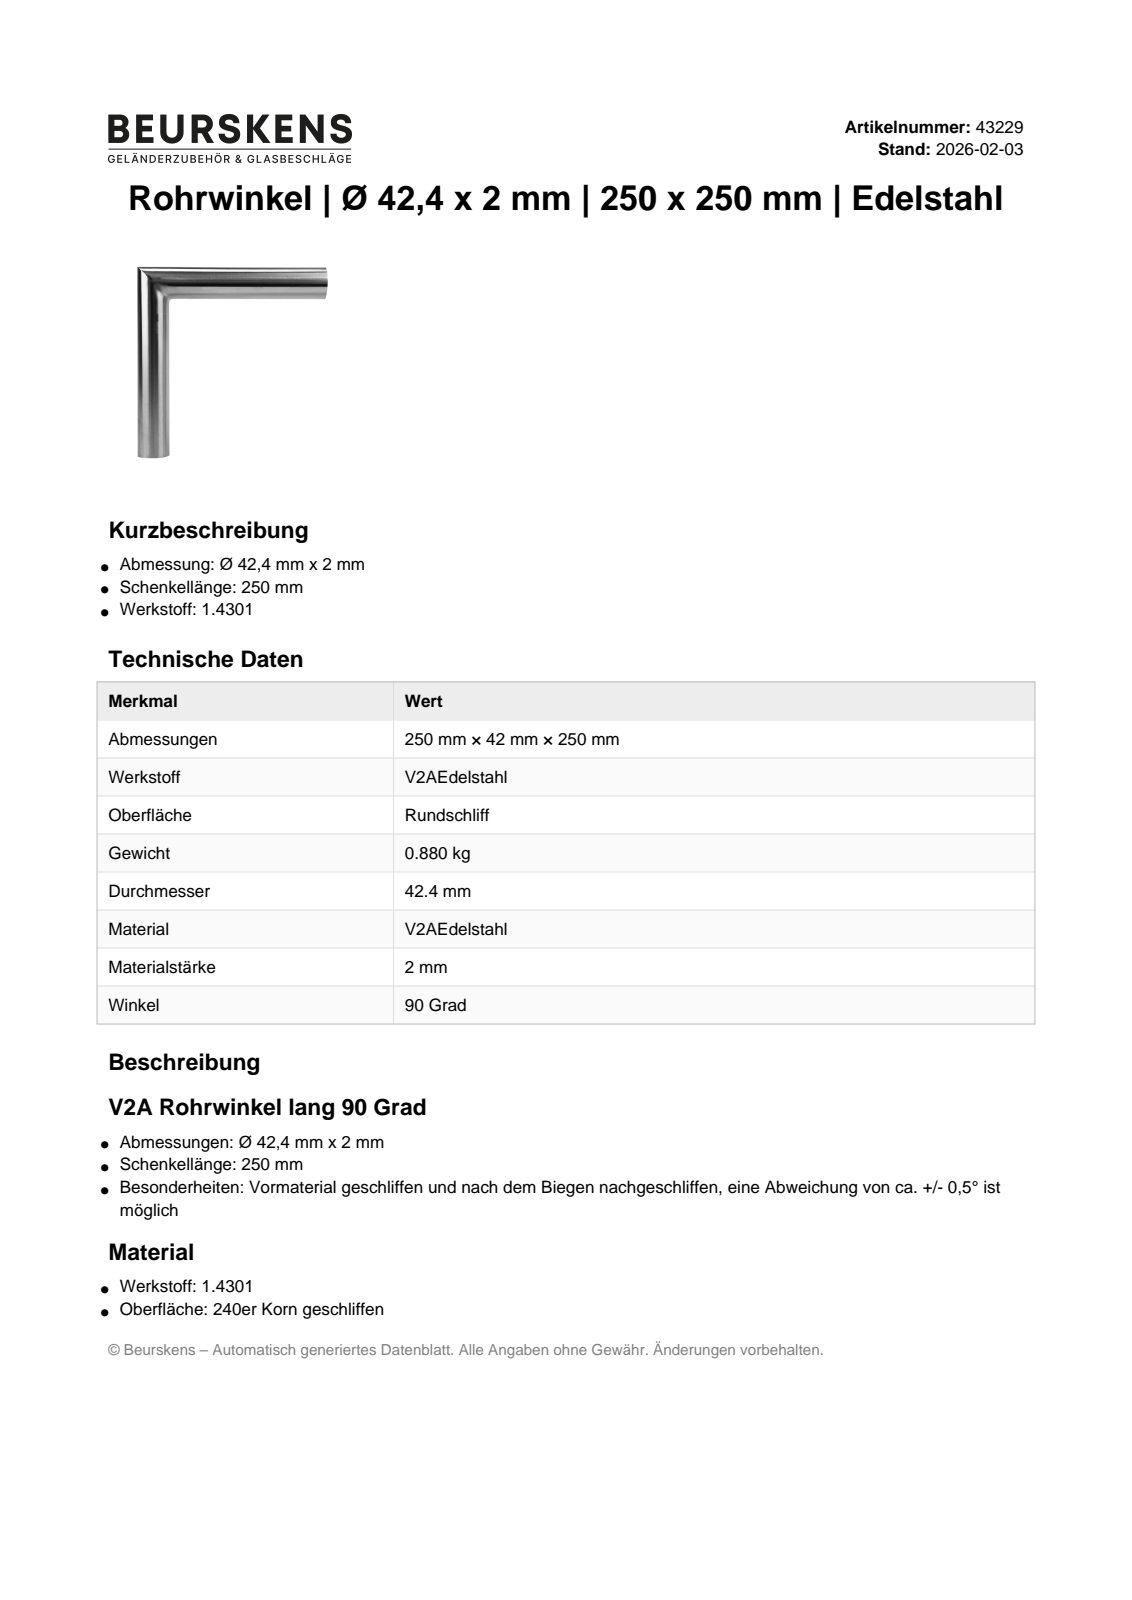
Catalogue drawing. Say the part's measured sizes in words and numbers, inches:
The part is named "43229". Its 3-D file was written by "Autodesk Inventor 2022 (AUTOMOTIVE_DESIGN)". It is 1 solid with 6 faces: 2 planar, 4 cylindrical and 0 other. Overall it measures 10.677 by 10.677 by 1.669 inches. Its volume is 7.745 cubic inches and its surface area 197.5 square inches. Round holes: 2 of diameter 1.512. Round bosses or shafts: 2 of diameter 1.669.
